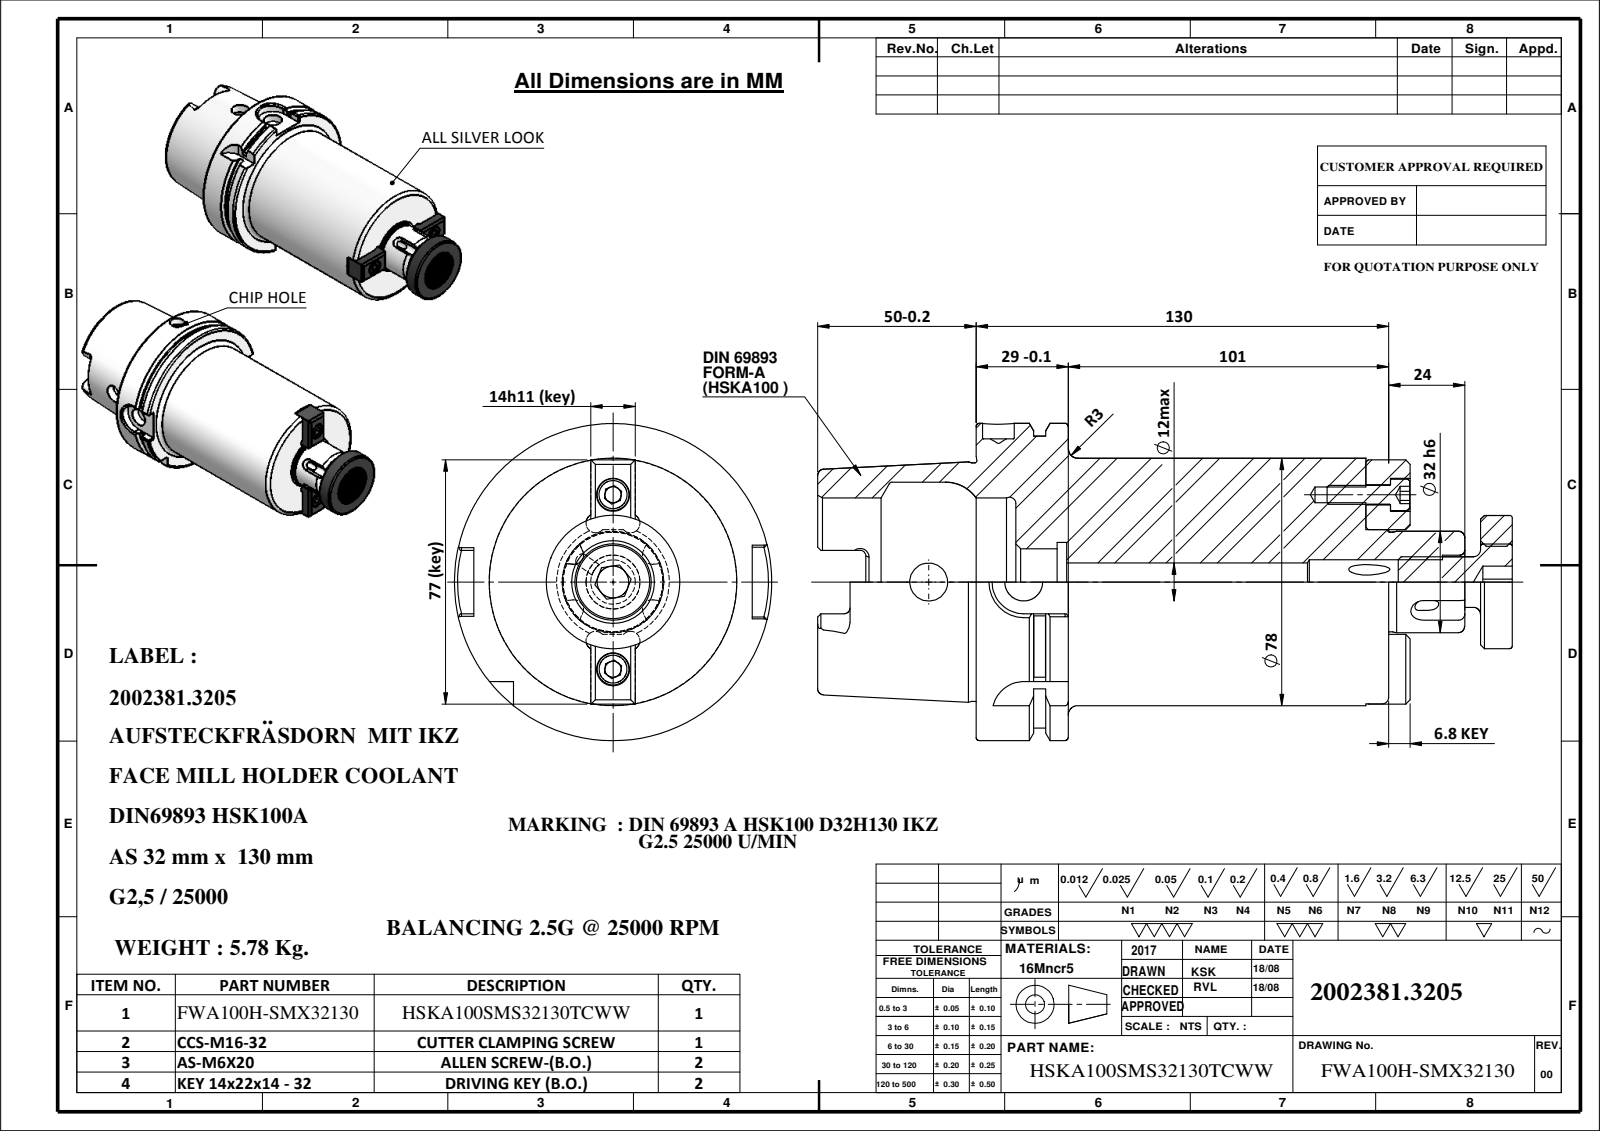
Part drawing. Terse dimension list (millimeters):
name: HSKA100SMS32130TCWW; KEY 14x22x14 - 32; 91100A-AS532130; CCS-M16-32 (+2 more)
written by: SolidWorks 2009 (CONFIG_CONTROL_DESIGN)
unit: mm
bodies: 7 solids, 389 faces (148 planar, 104 cylindrical, 137 other)
size: 219 × 100 × 100
volume: 758 988 mm³; area: 95 476 mm²
holes: 4× ⌀4, 3× ⌀12, 2× ⌀5, 2× ⌀6.4, 2× ⌀10.4, 1× ⌀10, 1× ⌀14, 1× ⌀17, 1× ⌀21, 1× ⌀22.5, 1× ⌀25, 1× ⌀53
bosses: 2× ⌀10, 2× ⌀6, 1× ⌀100, 1× ⌀92, 1× ⌀78, 1× ⌀75.16, 1× ⌀42, 1× ⌀32
rounds: 8× R3, 6× R1.8, 4× R4.88, 2× R10, 1× R11
face distances: 130, 29, 101, 12.5, 16.5, 117.5, 14, 169, 156.5, 140
hole spacings: 27.5, 30, 55
